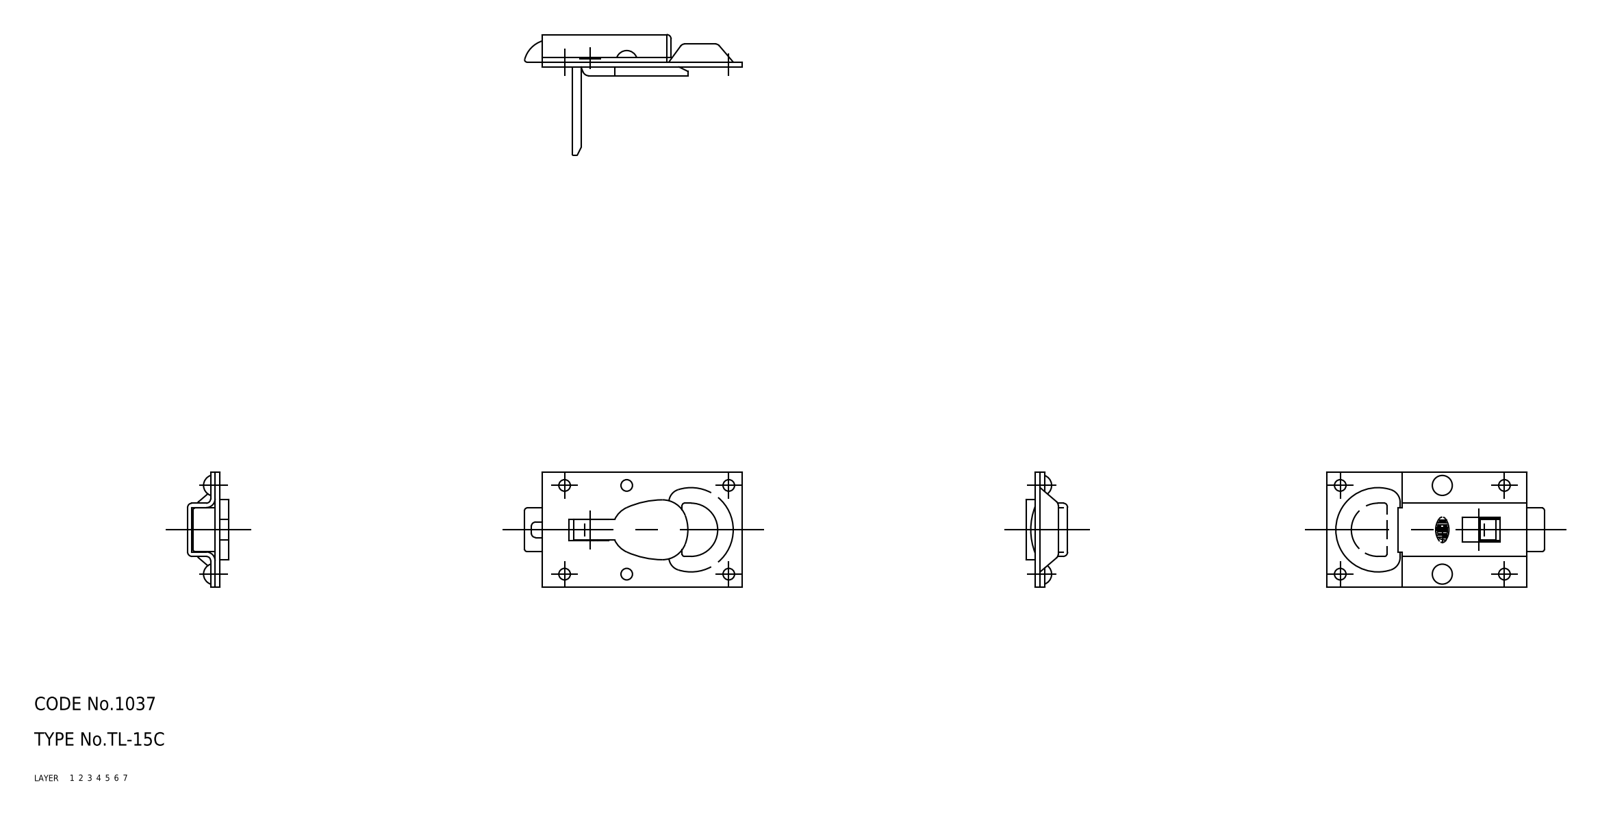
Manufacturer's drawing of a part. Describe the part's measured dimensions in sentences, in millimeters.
The part is named "rivet; shaft; lever; latch (+3 more)". Its 3-D file was written by "CADfix (AUTOMOTIVE_DESIGN)". It is 7 solids with 200 faces: 0 planar, 0 cylindrical and 200 other. Overall it measures 49 by 26 by 9.3 millimeters. Its volume is 3 360 cubic millimeters and its surface area 6 182 square millimeters.
